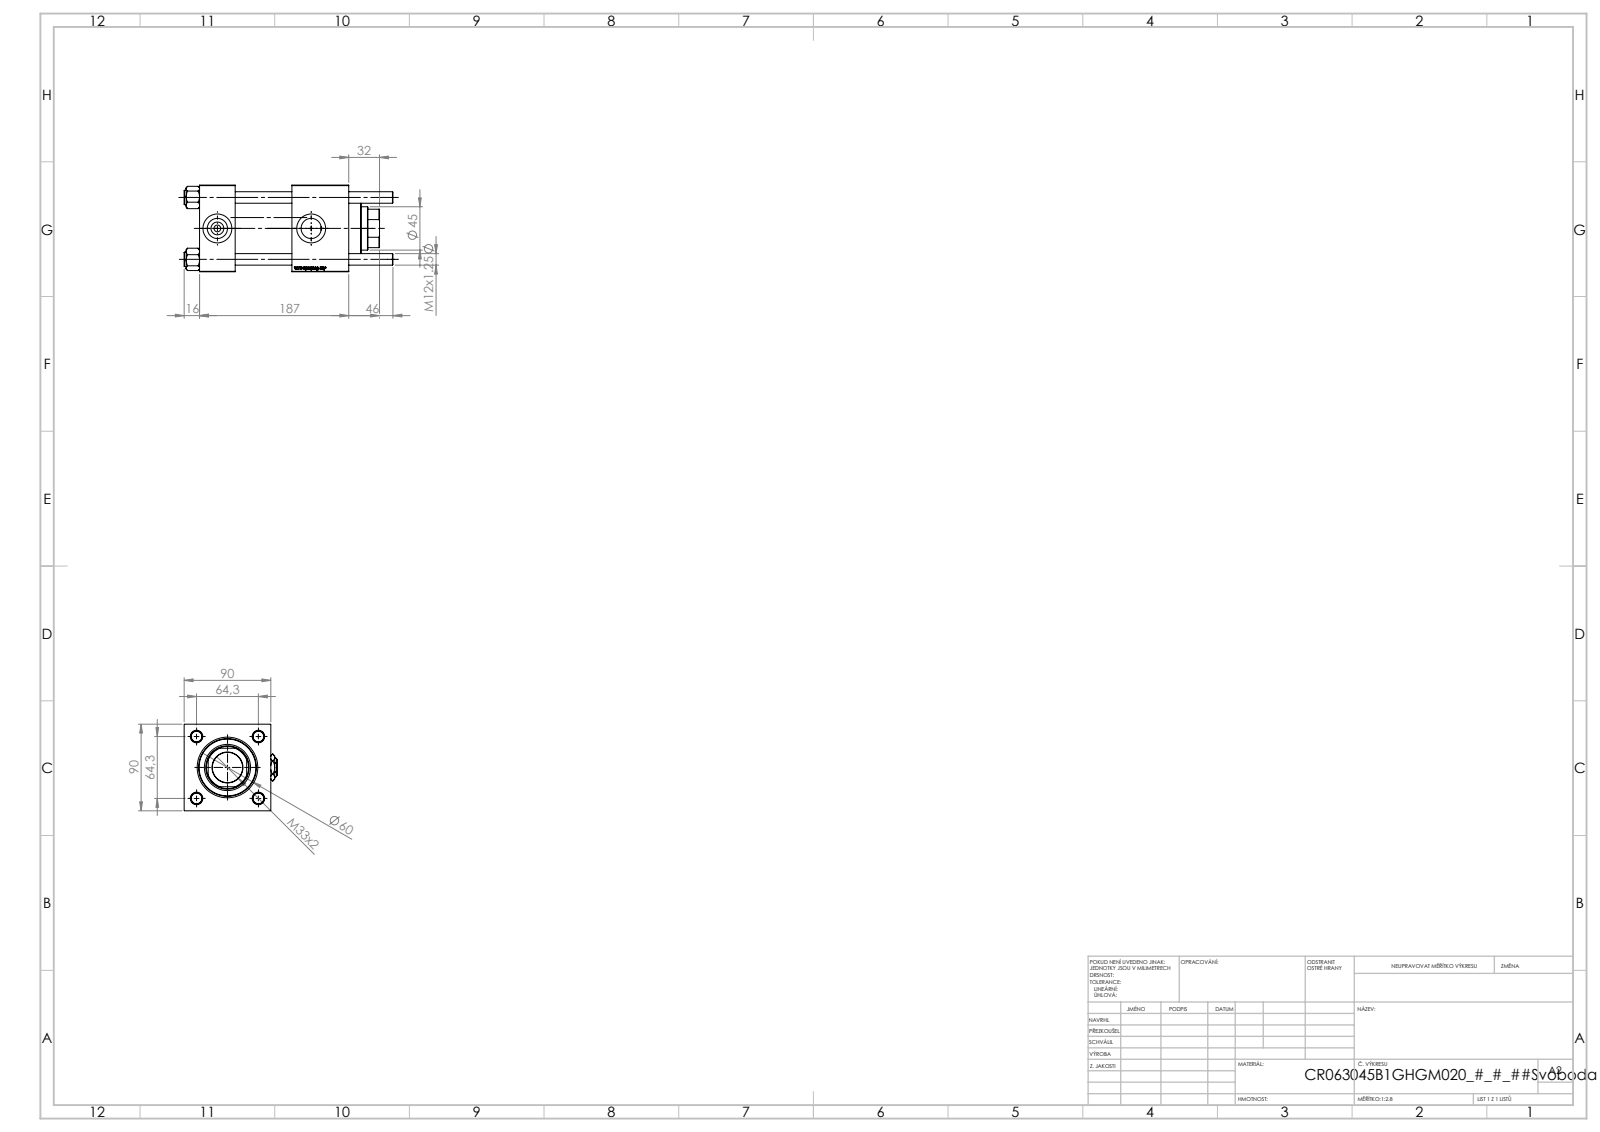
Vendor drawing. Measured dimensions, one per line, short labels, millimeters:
name: NUT_M5_B; V215_VC_A; V215CR_B-1; Zatka_pro_OIL_PORT (+2 more)
written by: SolidWorks 2019 (CONFIG_CONTROL_DESIGN)
unit: mm
bodies: 12 solids, 1202 faces (454 planar, 80 cylindrical, 668 other)
size: 217 × 97 × 90
volume: 1 028 000 mm³; area: 207 938 mm²
holes: 4× ⌀12, 2× ⌀7, 2× ⌀20.96, 2× ⌀30, 1× ⌀31.5, 1× ⌀45, 1× ⌀48, 1× ⌀50, 1× ⌀60, 1× ⌀63
bosses: 4× ⌀15, 1× ⌀69
rounds: 1× R22
face distances: 90, 59, 37, 96, 118, 155, 126.3, 89.3, 30.3, 28.7
hole spacings: 45.47, 64.3, 90.93, 97.5
